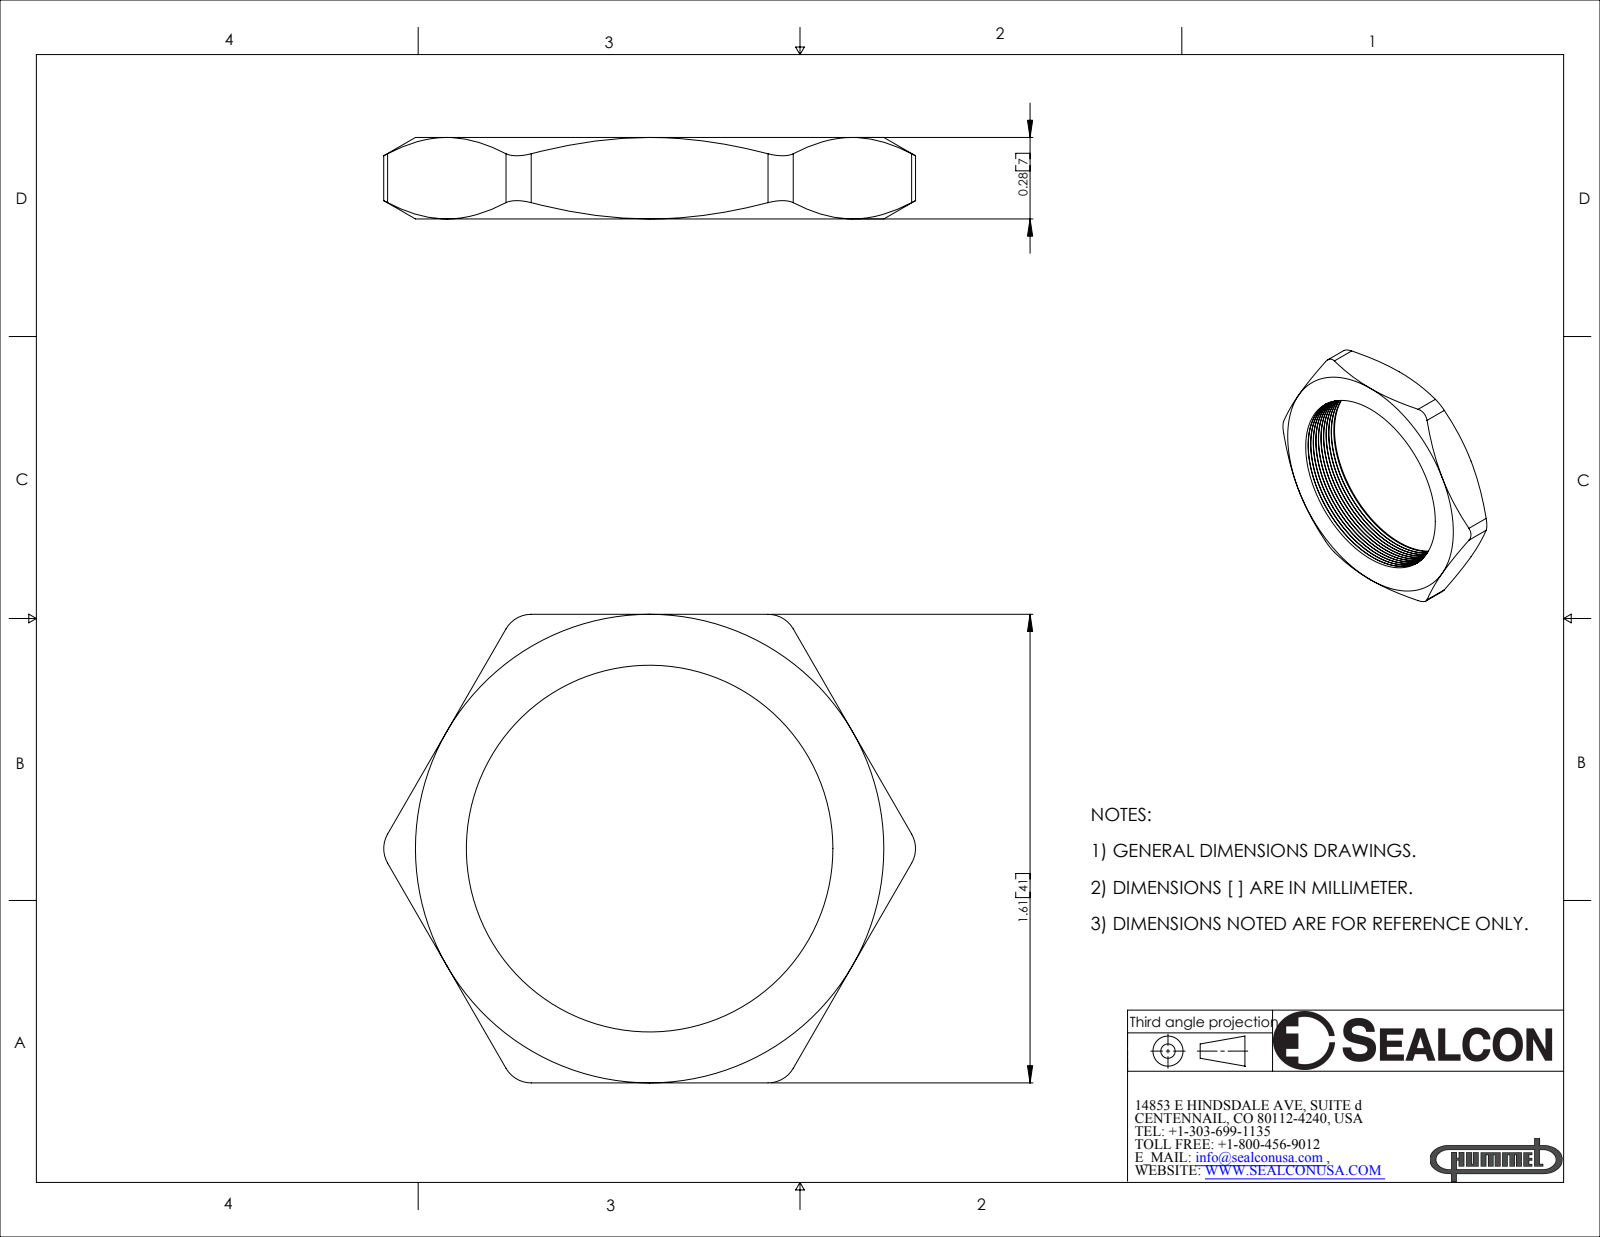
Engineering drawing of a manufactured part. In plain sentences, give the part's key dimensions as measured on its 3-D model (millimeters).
The part is named "NM-32". Its 3-D file was written by "SolidWorks 2007 (CONFIG_CONTROL_DESIGN)". It is 1 solid with 95 faces: 8 planar, 29 cylindrical and 58 other. Overall it measures 46.4 by 40.9 by 7.1 millimeters. Its volume is 4 260 cubic millimeters and its surface area 3 535 square millimeters. Round holes: 1 of diameter 32. Partial cylindrical surfaces (rounded edges, fillets, slot ends): 6 of radius 2.5. The main face-to-face distances are 7.1, 40.9.
